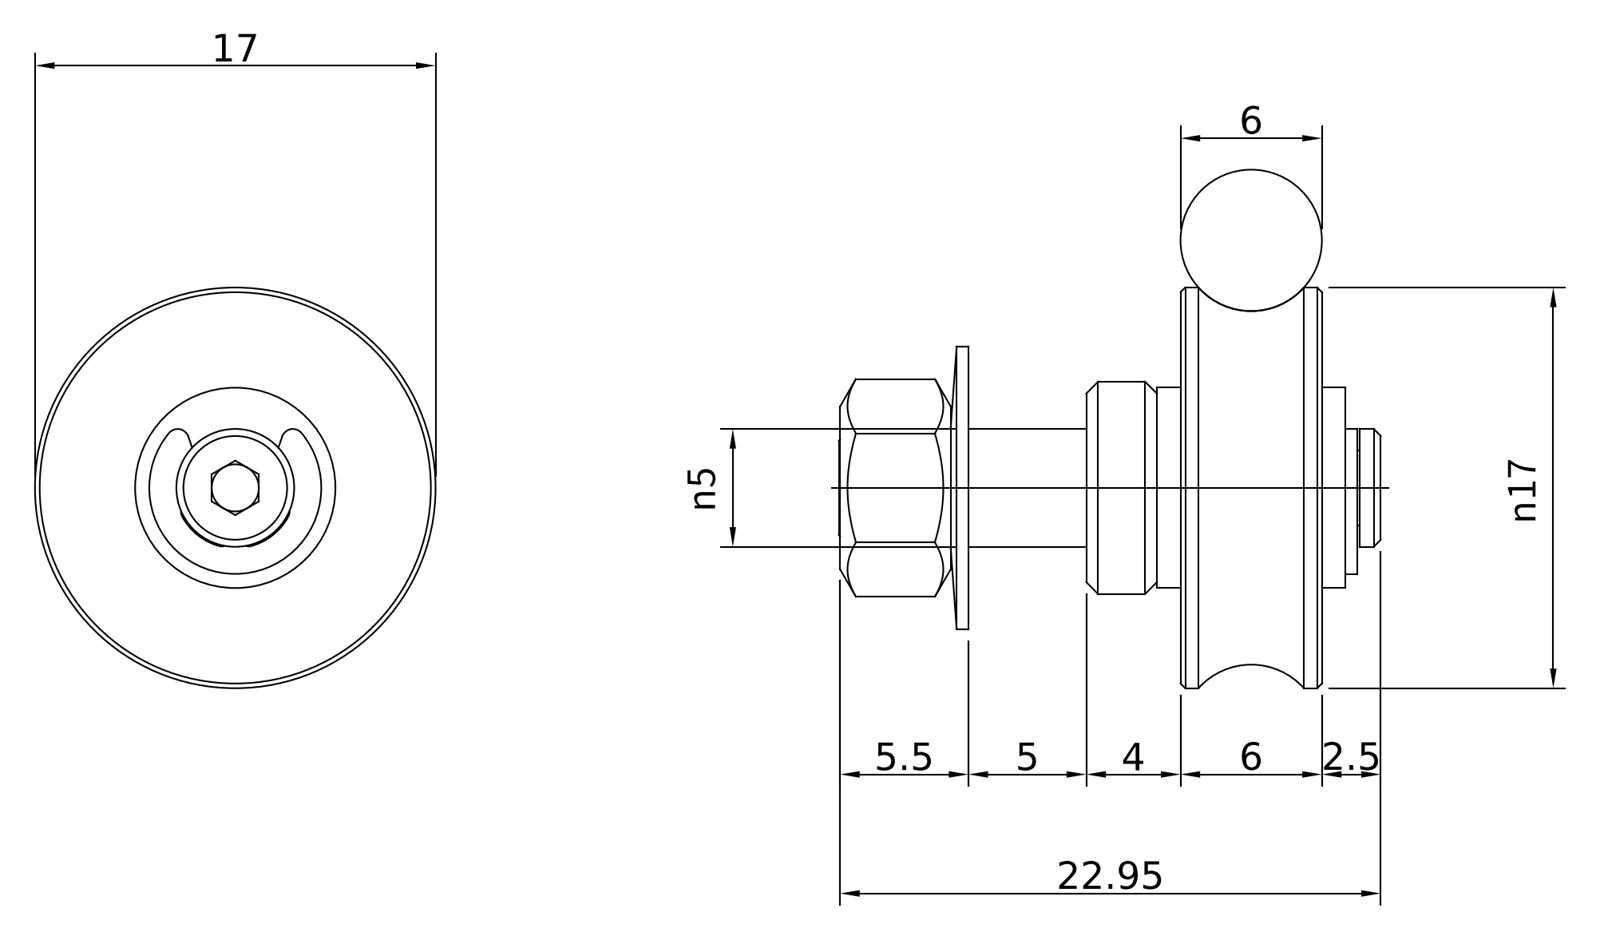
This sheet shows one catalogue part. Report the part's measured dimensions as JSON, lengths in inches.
{"part_name": "23.517.00C; 70PE00124-A; 80RT00012R-A; 80MTZ0006-A (+2 more)", "step_written_by": "Autodesk Inventor 2022 (AUTOMOTIVE_DESIGN)", "units": "inches", "bodies": {"solids": 5, "faces": 94, "planar": 50, "cylindrical": 29, "other": 15}, "overall_size": [0.906, 0.669, 0.669], "volume_in3": 0.118, "surface_area_in2": 3.139, "round_holes": [[0.079, 1], [0.126, 1], [0.163, 1], [0.205, 1]], "round_bosses_or_shafts": [[0.669, 1], [0.472, 1], [0.354, 1], [0.335, 1], [0.197, 1]], "partial_cylinders_radius": [[0.01, 2], [0.015, 2], [0.019, 2], [0.013, 1], [0.101, 1], [0.144, 1]], "face_to_face_distances": [0.236, 0.039, 0.276, 0.315, 0.118, 0.197, 0.035, 0.335, 0.059, 0.024]}
